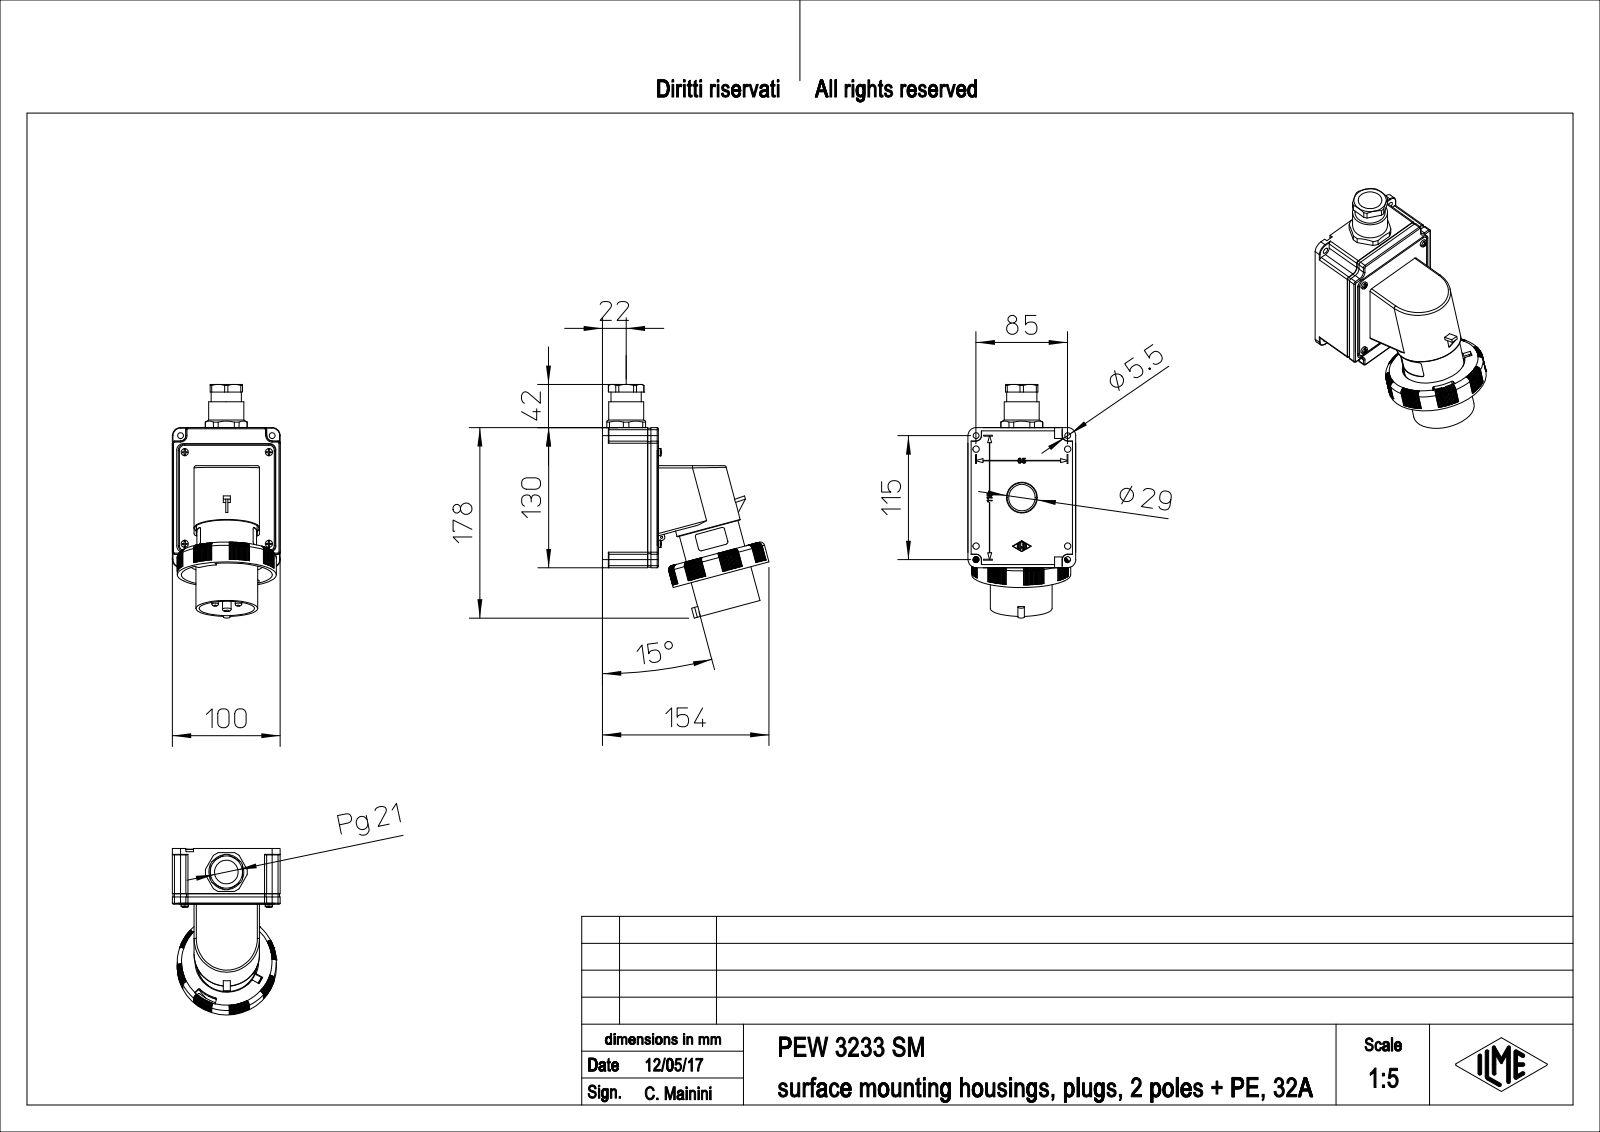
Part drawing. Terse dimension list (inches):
name: PEW_3233_SM
written by: PTC Creo Elements/Direct Modeling 19.0E 27-Jun-2016 (C) Parametric Technology GmbH (AUTOMOTIVE_DESIGN)
unit: in
bodies: 1 solid, 1809 faces (910 planar, 379 cylindrical, 520 other)
size: 8.531 × 6.085 × 3.937
volume: 59.31 in³; area: 242.9 in²
holes: 8× ⌀0.217, 4× ⌀0.236, 2× ⌀0.157, 2× ⌀0.165, 2× ⌀0.24, 2× ⌀1.126, 1× ⌀0.079, 1× ⌀0.866, 1× ⌀3.327
bosses: 6× ⌀0.264, 2× ⌀0.236, 2× ⌀0.118, 1× ⌀3.622, 1× ⌀2.756, 1× ⌀2.39, 1× ⌀2.256, 1× ⌀2.213
rounds: 136× R0.142, 18× R0.02, 10× R0.039, 10× R0.079, 10× R1.635, 8× R0.059, 8× R0.236, 4× R0.012
face distances: 0.079, 0.177, 1.744, 2, 0.256, 1.823, 0.118, 3.937, 3.726, 0.27
hole spacings: 0.492, 3.346, 2.437, 2.815, 3.382, 4.035, 5.243, 0.827
